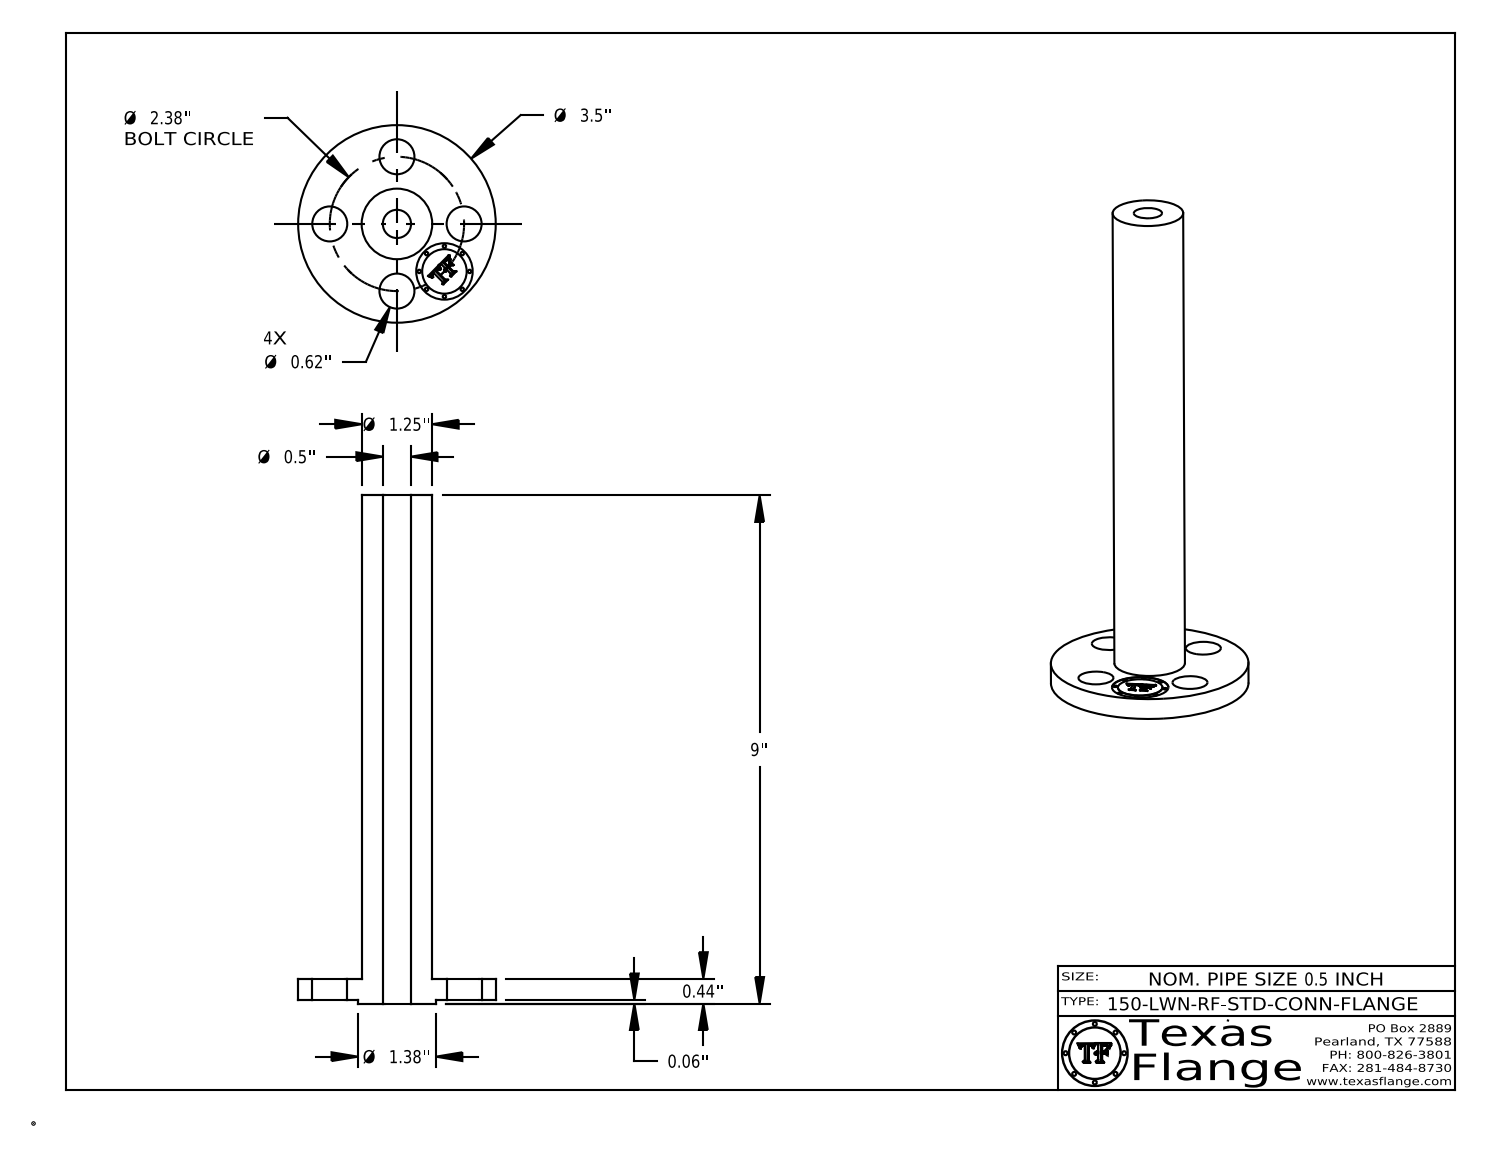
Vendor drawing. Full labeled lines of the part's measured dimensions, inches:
Part name (STEP PRODUCT): 0.5-150-LWN-RF-STD-CONN-FLANGE
STEP written by: CATIA V5 STEP AP214 (AUTOMOTIVE_DESIGN)
Units: inches
Bodies: 1 solid, 405 faces (369 planar, 36 cylindrical, 0 other)
Overall size (bounding box): 9 × 3.5 × 3.5
Volume: 12.01 in³ · Surface area: 71.61 in²
Round holes (diameter × count): ⌀0.62 ×4, ⌀0.5 ×1, ⌀1 ×1
Round bosses / shafts (diameter × count): ⌀0.061 ×8, ⌀3.5 ×1, ⌀1.38 ×1, ⌀1.25 ×1, ⌀0.788 ×1
Main face-to-face distances: 0.378, 0.063, 0.44, 9, 8.937, 8.56, 0.435, 0.372, 8.565, 0.298
Hole centre spacings: 1.19, 1.683, 0.911, 2.199, 2.38, 1.19
